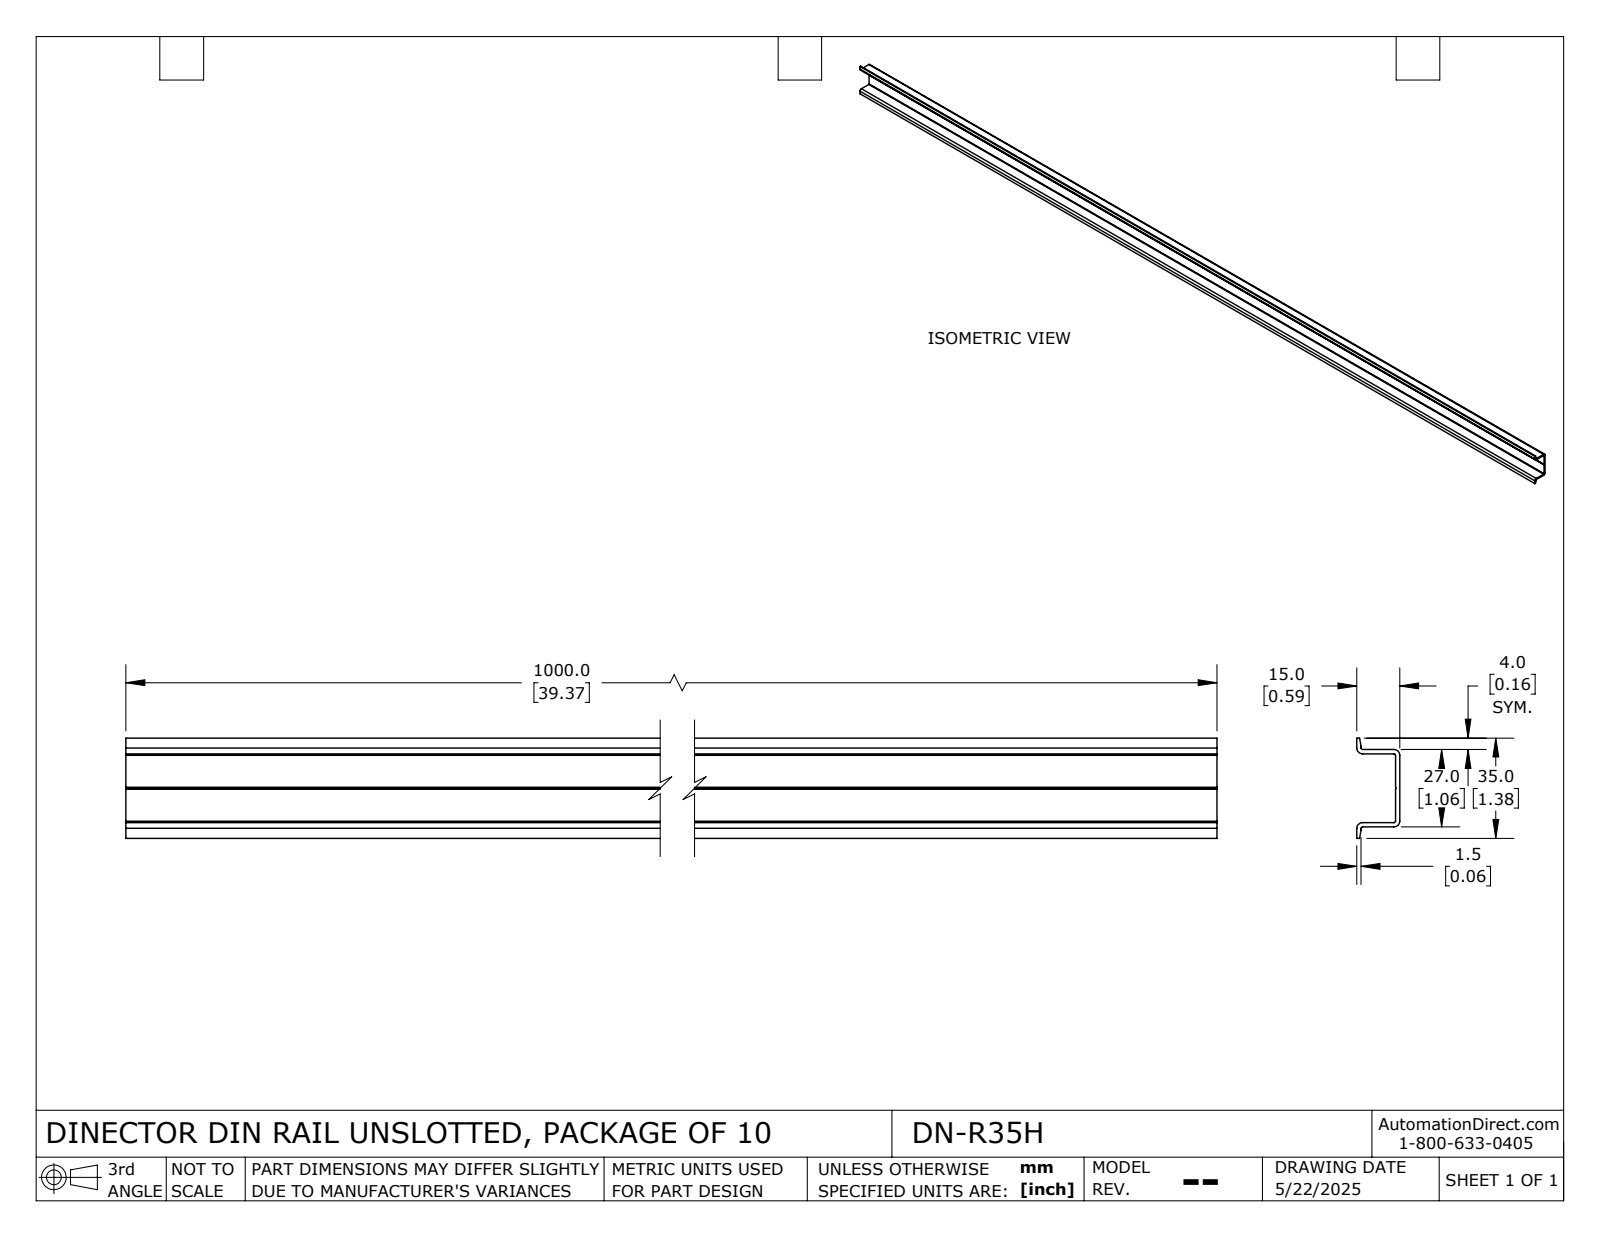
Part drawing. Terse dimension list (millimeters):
name: DN-R35HS_Default
written by: SolidWorks 2024 (CONFIG_CONTROL_DESIGN)
unit: mm
bodies: 1 solid, 27 faces (19 planar, 8 cylindrical, 0 other)
size: 1000 × 35 × 15
volume: 88 292 mm³; area: 122 079 mm²
rounds: 4× R0.5, 4× R2
face distances: 1.5, 25.5, 27, 24, 13.5, 15, 4, 5.5, 29.5, 31
